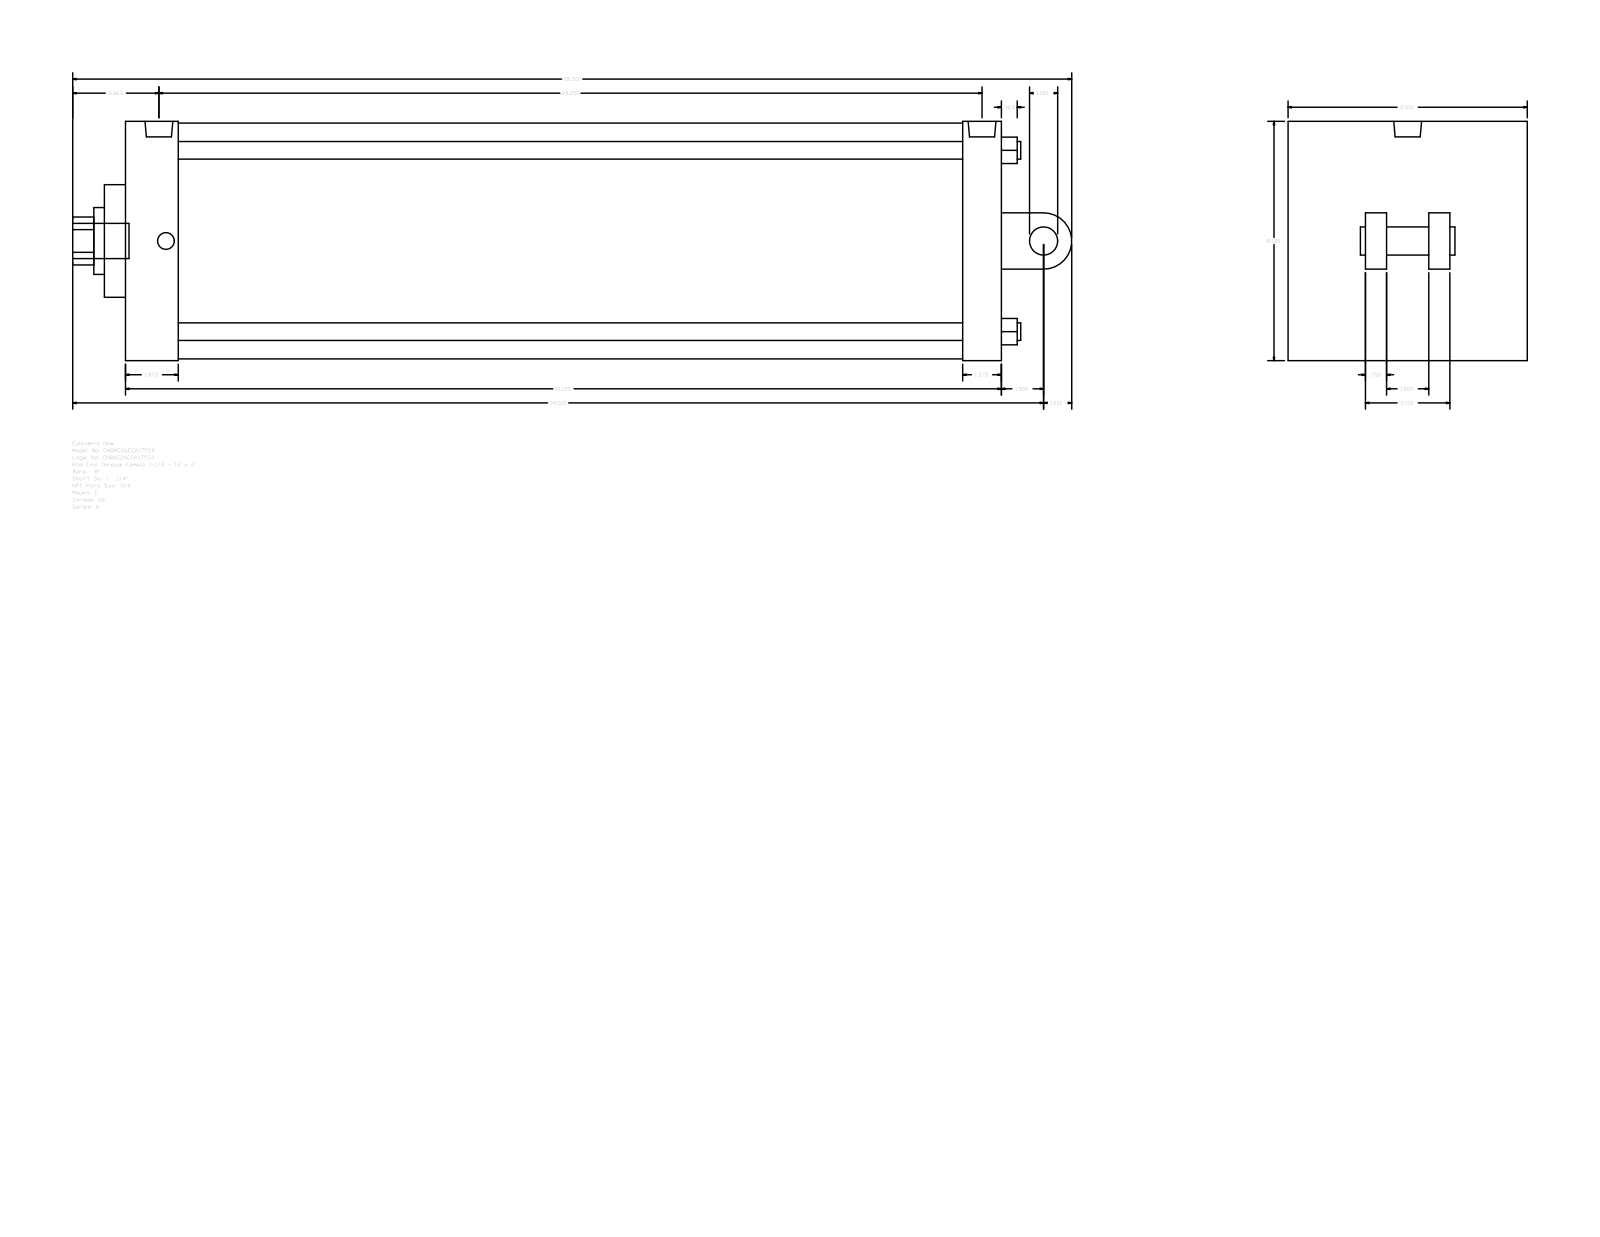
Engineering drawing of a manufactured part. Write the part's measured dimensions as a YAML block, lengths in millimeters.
part_name: "A_C__0800_1.75"
step_written_by: "GSSL Pune (CONFIG_CONTROL_DESIGN)"
units: millimeters
bodies: {solids: 0, faces: 104, planar: 75, cylindrical: 29, other: 0}
overall_size: [901.7, 215.9, 215.9]
round_holes:
  - {diameter: 15.88, count: 4}
  - {diameter: 15.08, count: 2}
  - {diameter: 25.12, count: 1}
  - {diameter: 44.45, count: 1}
  - {diameter: 60.33, count: 1}
  - {diameter: 212.72, count: 1}
round_bosses_or_shafts:
  - {diameter: 15.08, count: 2}
  - {diameter: 31.75, count: 1}
  - {diameter: 25.4, count: 1}
  - {diameter: 25.12, count: 1}
partial_cylinders:
  - {radius: 21.63, count: 1}
  - {radius: 25.4, count: 1}
face_to_face_distances: [790.58, 215.9, 19.05, 57.15, 47.63, 742.95, 755.65, 708.02, 34.93, 88.9]
hole_center_spacings: [115.67, 163.58, 231.34, 6.35]
